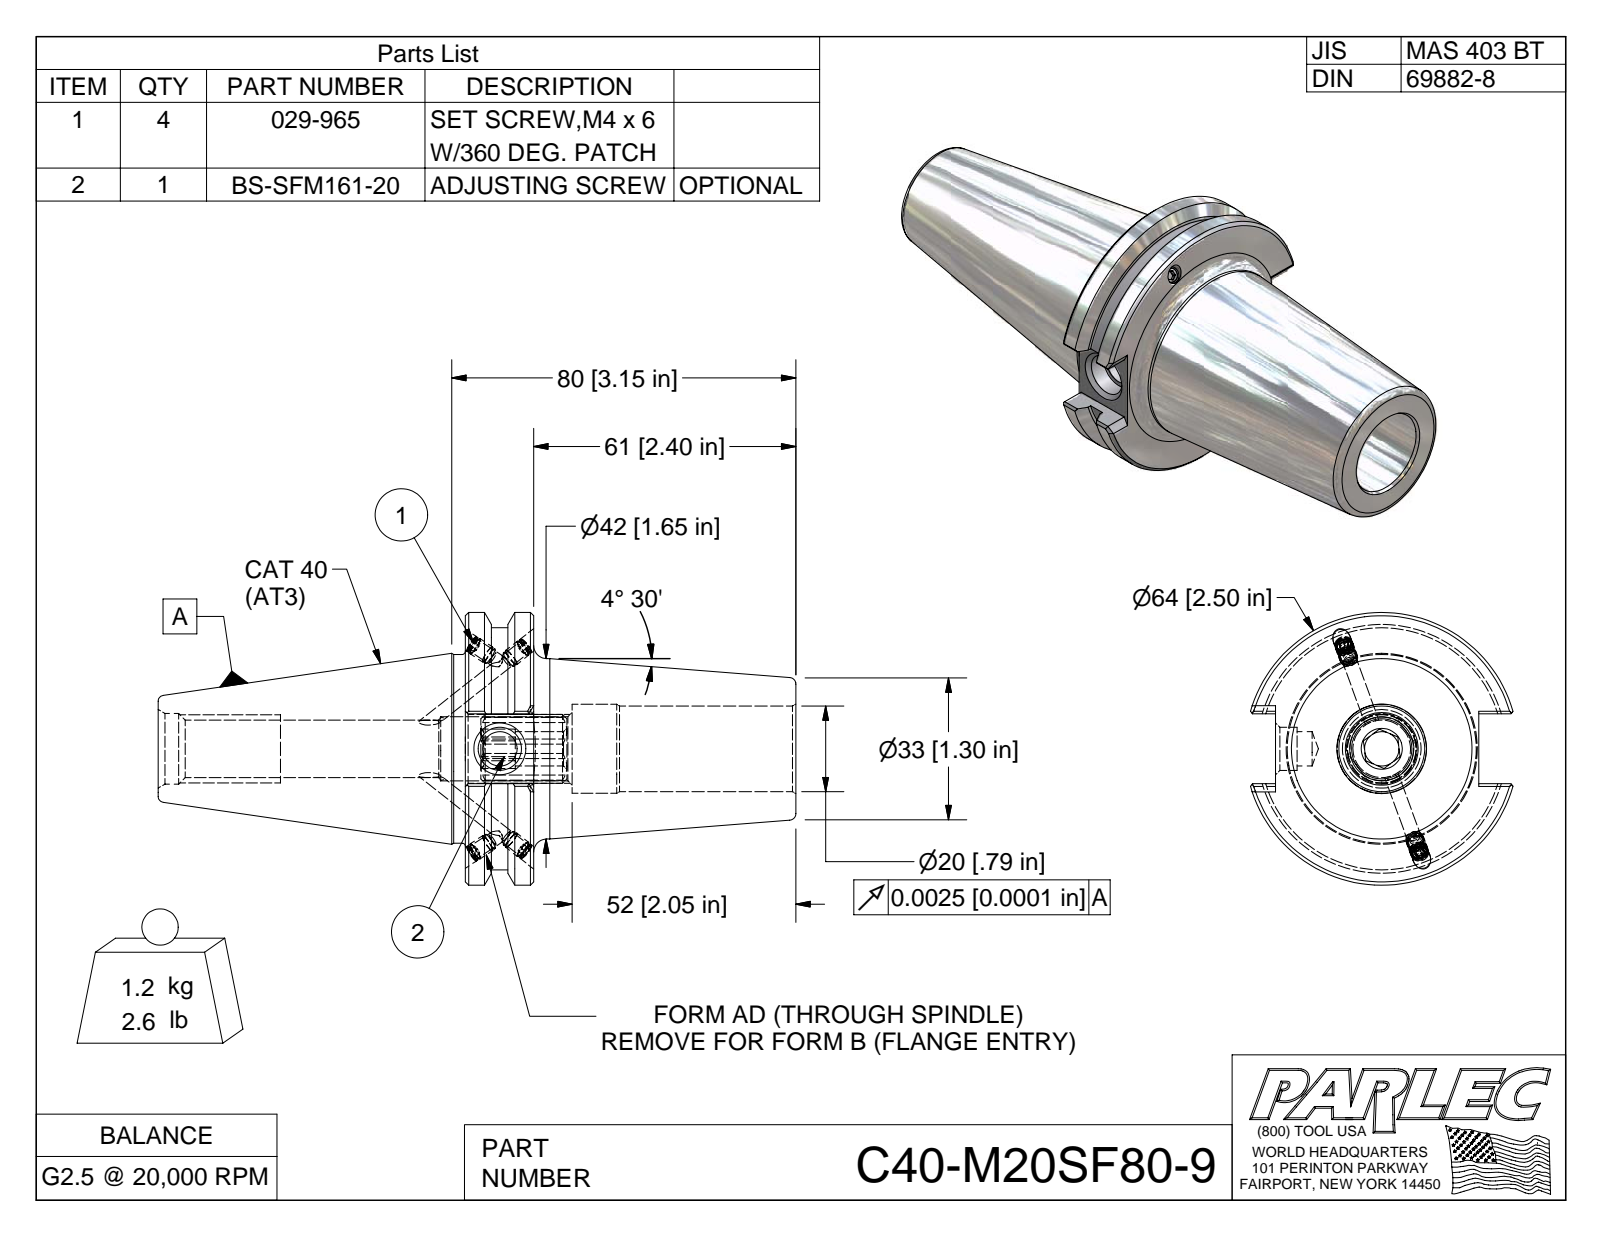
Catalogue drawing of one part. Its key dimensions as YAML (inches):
part_name: "C40-M20SF80-9; C40BC-M20SF80-9-1; 029-965; BS-SFM161-20"
step_written_by: "Autodesk Inventor 2009 (AUTOMOTIVE_DESIGN)"
units: inches
bodies: {solids: 6, faces: 173, planar: 87, cylindrical: 32, other: 54}
overall_size: [5.837, 2.5, 2.403]
volume: 9.314
surface_area: 51.78
round_holes:
  - {diameter: 0.13, count: 4}
  - {diameter: 0.161, count: 4}
  - {diameter: 0.786, count: 1}
  - {diameter: 0.816, count: 1}
round_bosses_or_shafts:
  - {diameter: 0.165, count: 4}
  - {diameter: 0.157, count: 4}
  - {diameter: 2.5, count: 1}
  - {diameter: 2.219, count: 1}
  - {diameter: 1.73, count: 1}
  - {diameter: 1.654, count: 1}
partial_cylinders:
  - {radius: 0.315, count: 1}
face_to_face_distances: [0.625, 3.025, 2.4, 0.64, 0.551, 1.86, 2.812, 3.437, 5.837, 3.201]
